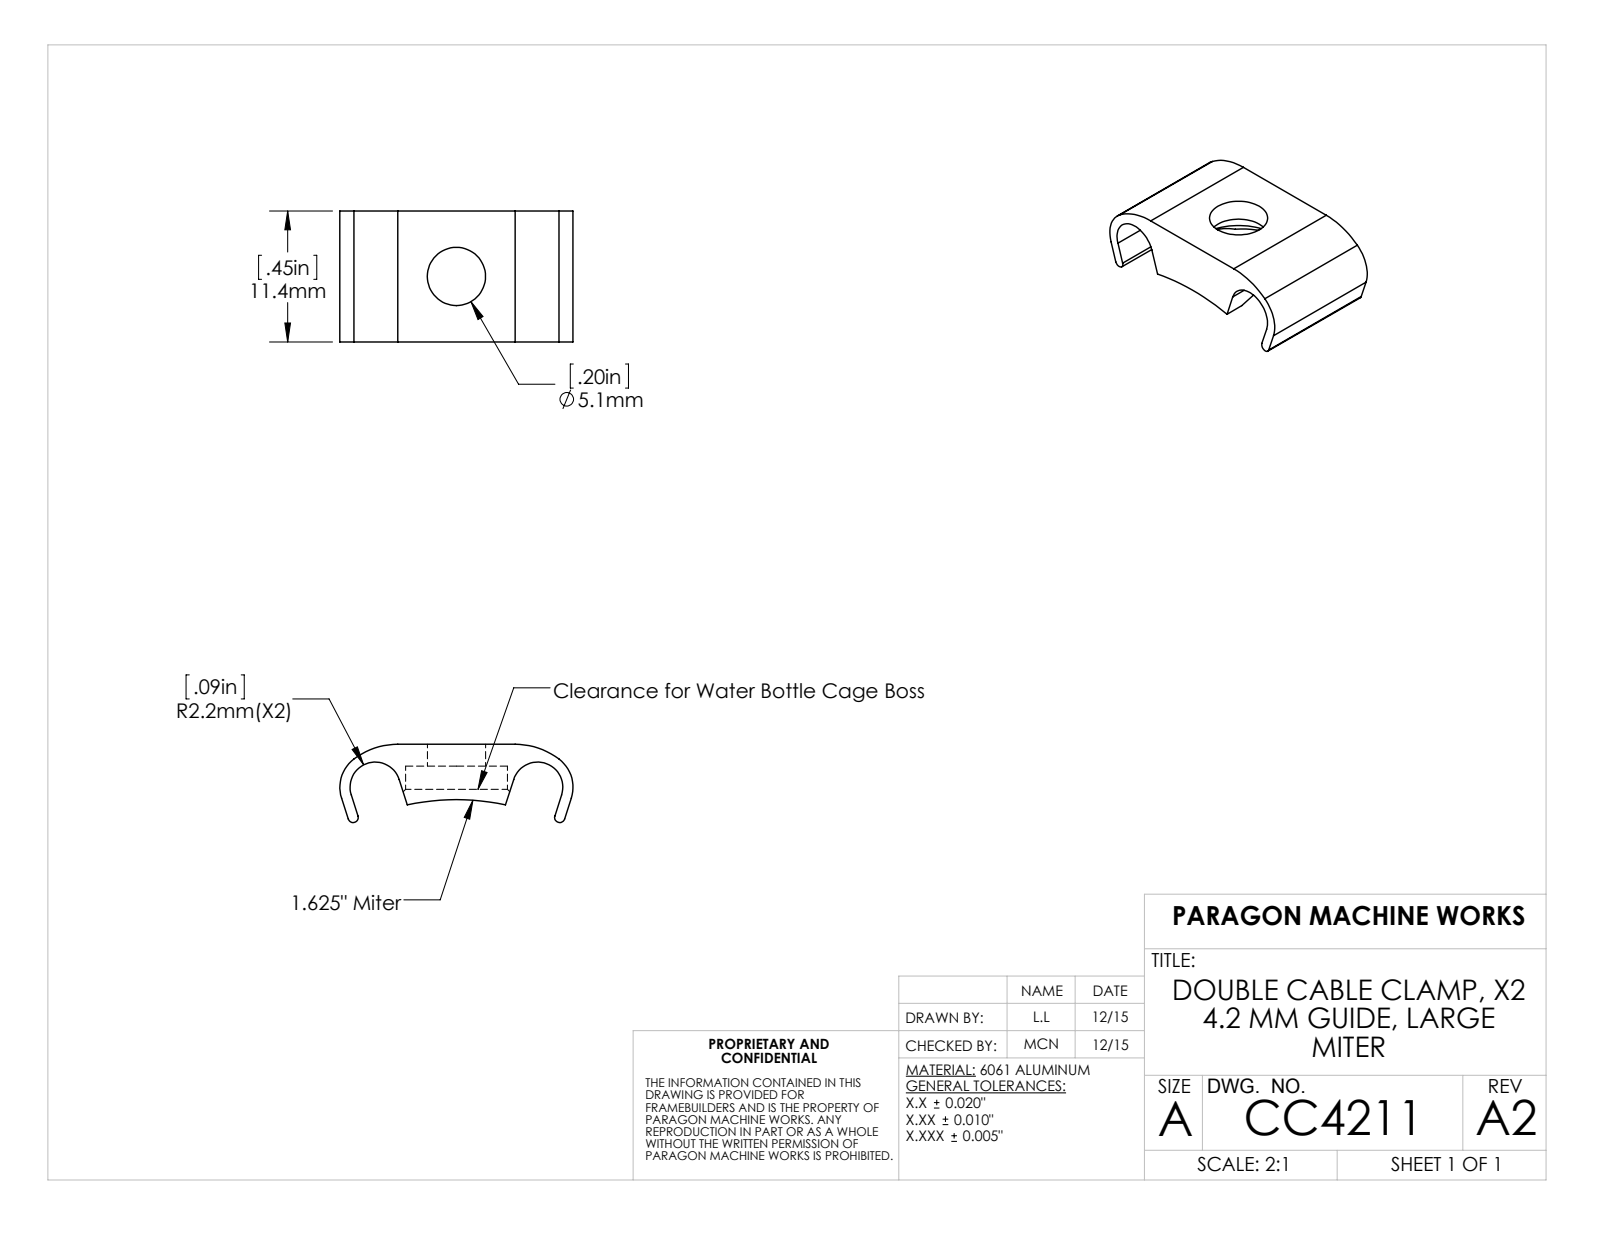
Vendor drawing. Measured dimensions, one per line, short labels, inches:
name: CC4211
written by: SolidWorks 2015 (AUTOMOTIVE_DESIGN)
unit: in
bodies: 1 solid, 29 faces (10 planar, 17 cylindrical, 2 other)
size: 0.801 × 0.45 × 0.269
volume: 0.034 in³; area: 1.419 in²
holes: 1× ⌀0.2, 1× ⌀0.35
rounds: 2× R0.018, 2× R0.087, 2× R0.122, 2× R0.25, 1× R0.823
face distances: 0.45, 0.035, 0.075, 0.173, 0.208
